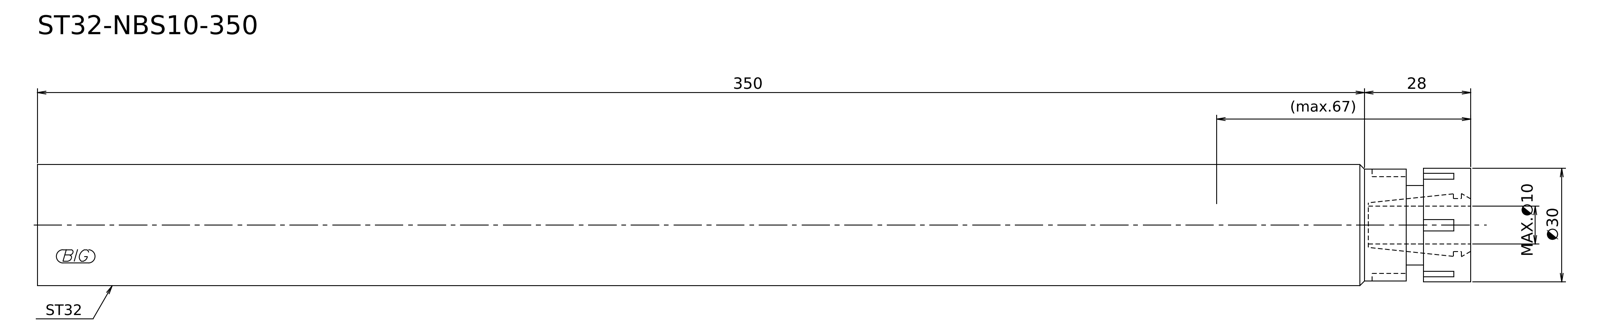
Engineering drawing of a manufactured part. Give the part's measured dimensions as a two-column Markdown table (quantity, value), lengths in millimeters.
| quantity | value |
| --- | --- |
| STEP written by | Kubotek KeyCreator V8.5.1 (14335) (CONFIG_CONTROL_DESIGN) |
| units | millimeters |
| bodies | 1 solid, 9 faces (4 planar, 4 cylindrical, 1 other) |
| overall size | 378 × 32 × 32 |
| volume | 299 323 mm³ |
| surface area | 39 934 mm² |
| round bosses / shafts (diameter × count) | 32 × 1, 30 × 1, 29.5 × 1, 21 × 1 |
| main face-to-face distances | 378, 12.5, 365.5, 17, 4.5, 361 |
